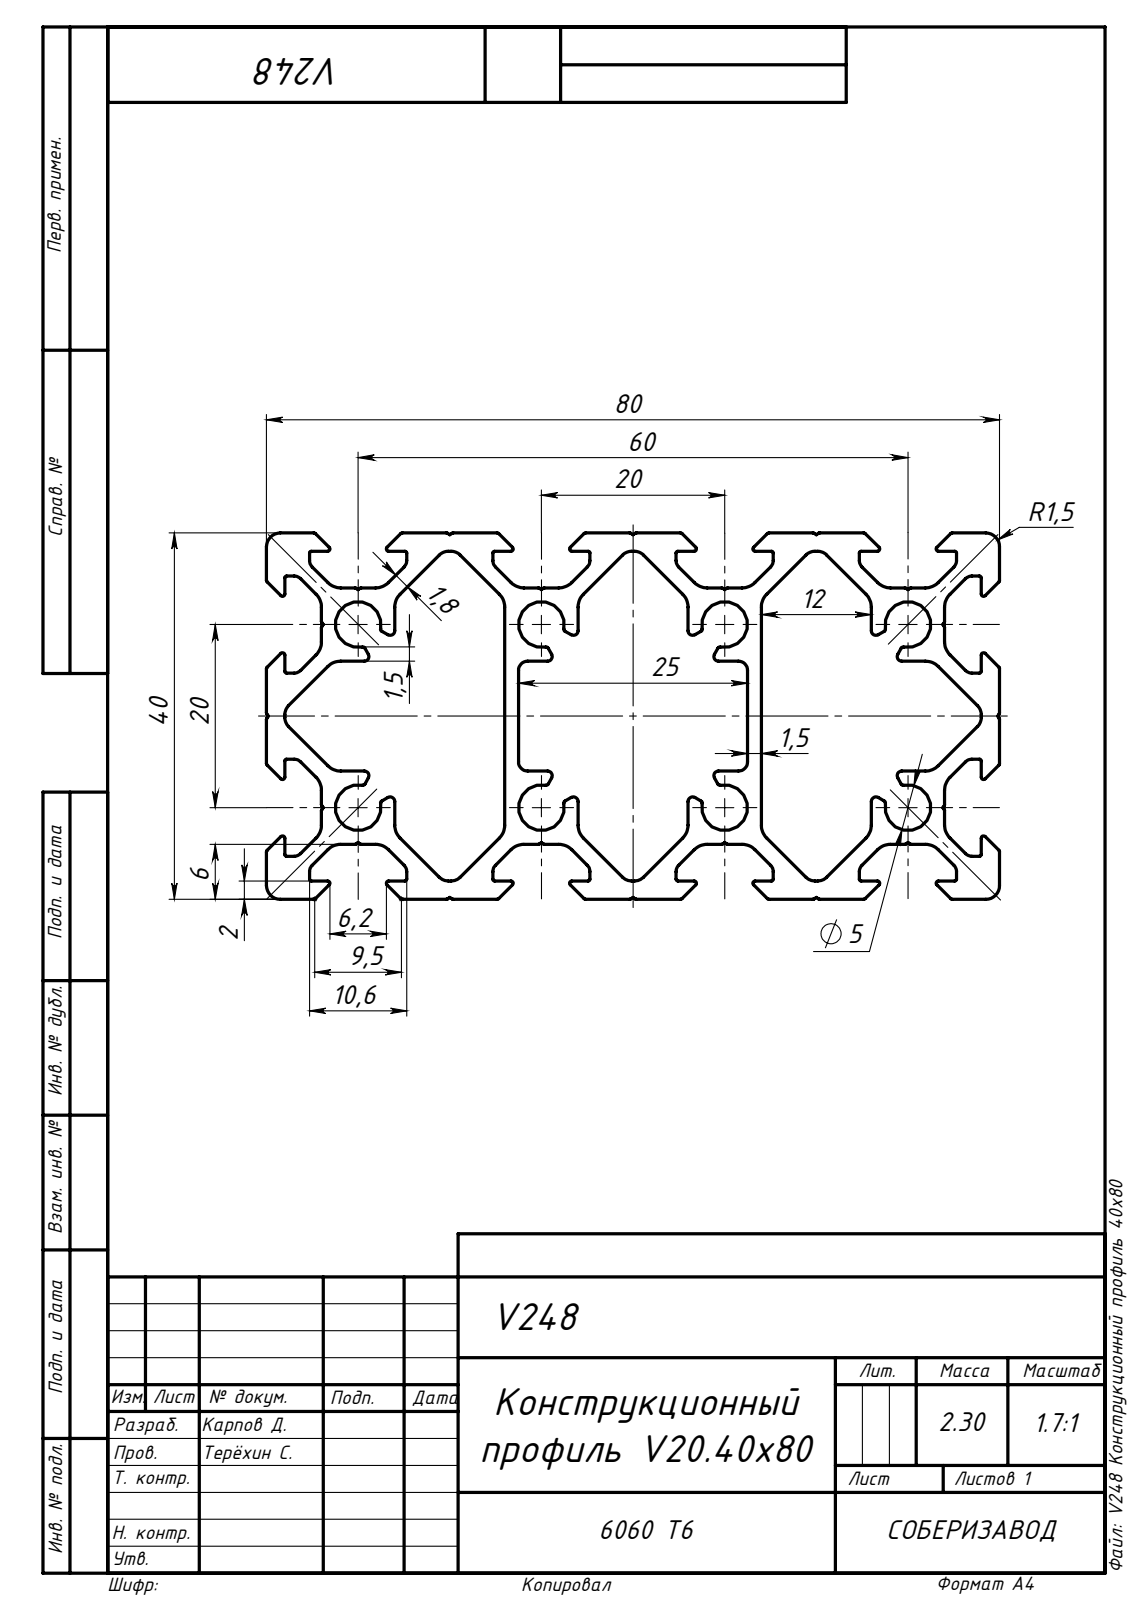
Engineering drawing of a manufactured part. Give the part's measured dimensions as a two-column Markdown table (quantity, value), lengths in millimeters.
| quantity | value |
| --- | --- |
| part name | 248 Конструкционный профиль 40х80 |
| STEP written by | SolidWorks 2014 (AUTOMOTIVE_DESIGN) |
| units | millimeters |
| bodies | 1 solid, 518 faces (246 planar, 272 cylindrical, 0 other) |
| overall size | 1000 × 80 × 40 |
| volume | 853 359 mm³ |
| surface area | 815 784 mm² |
| round holes (diameter × count) | 5 × 8 |
| partial cylindrical surfaces (radius × count) | 0.25 × 104, 2 × 40, 1 × 28, 0.2 × 24, 0.5 × 16, 1.4 × 16, 1.5 × 4 |
| main face-to-face distances | 14.14, 28.28, 20, 40, 1.8, 12, 12.34, 26, 2.83, 4.63 |
| hole center spacings | 20, 28.28, 40, 44.72, 60, 63.25 |
